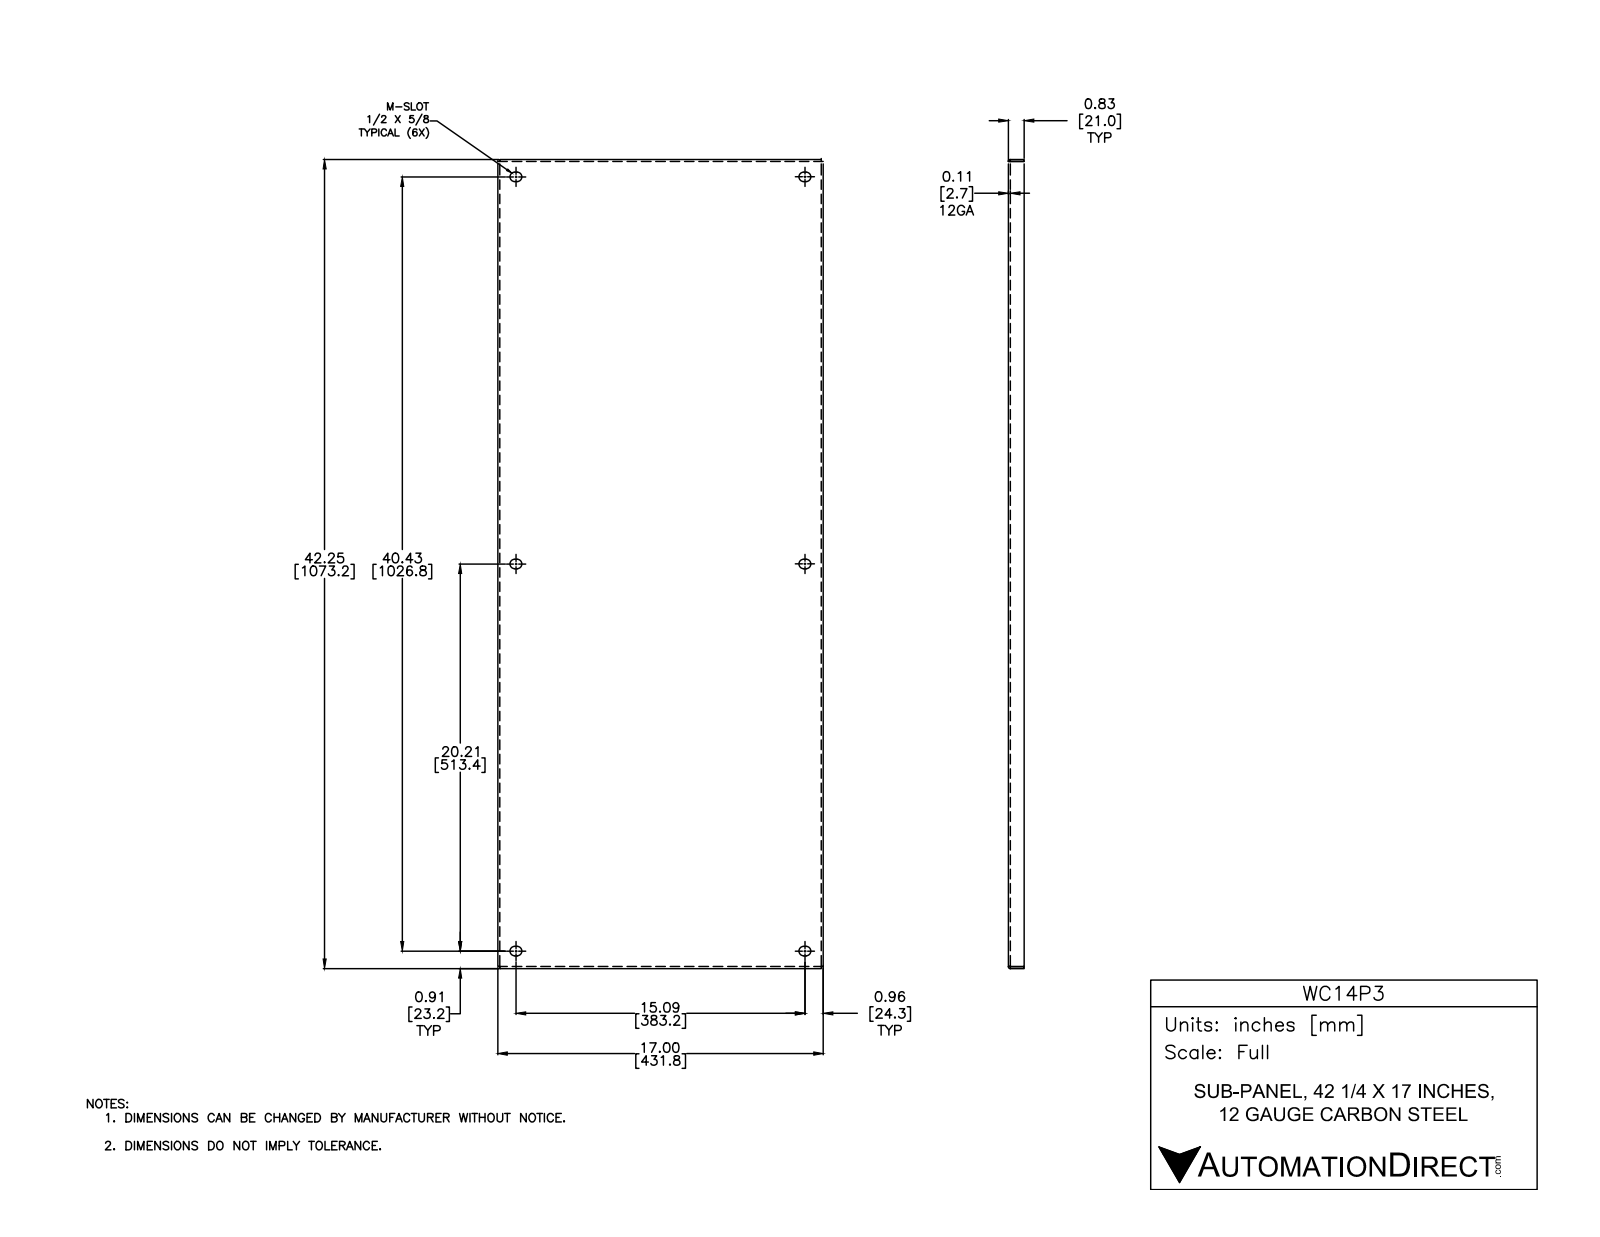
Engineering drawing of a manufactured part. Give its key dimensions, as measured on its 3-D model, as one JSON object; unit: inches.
{"part_name": "WC14P3", "step_written_by": "SolidWorks 2014 (AUTOMOTIVE_DESIGN)", "units": "inches", "bodies": {"solids": 1, "faces": 68, "planar": 34, "cylindrical": 26, "other": 8}, "overall_size": [42.125, 17.063, 0.828], "volume_in3": 83.61, "surface_area_in2": 1613, "partial_cylinders_radius": [[0.25, 12], [0.107, 3], [0.108, 1]], "face_to_face_distances": [0.105, 16.958, 17.063, 16.853, 0.828, 0.723, 0.104, 42.02, 42.125, 41.916]}
